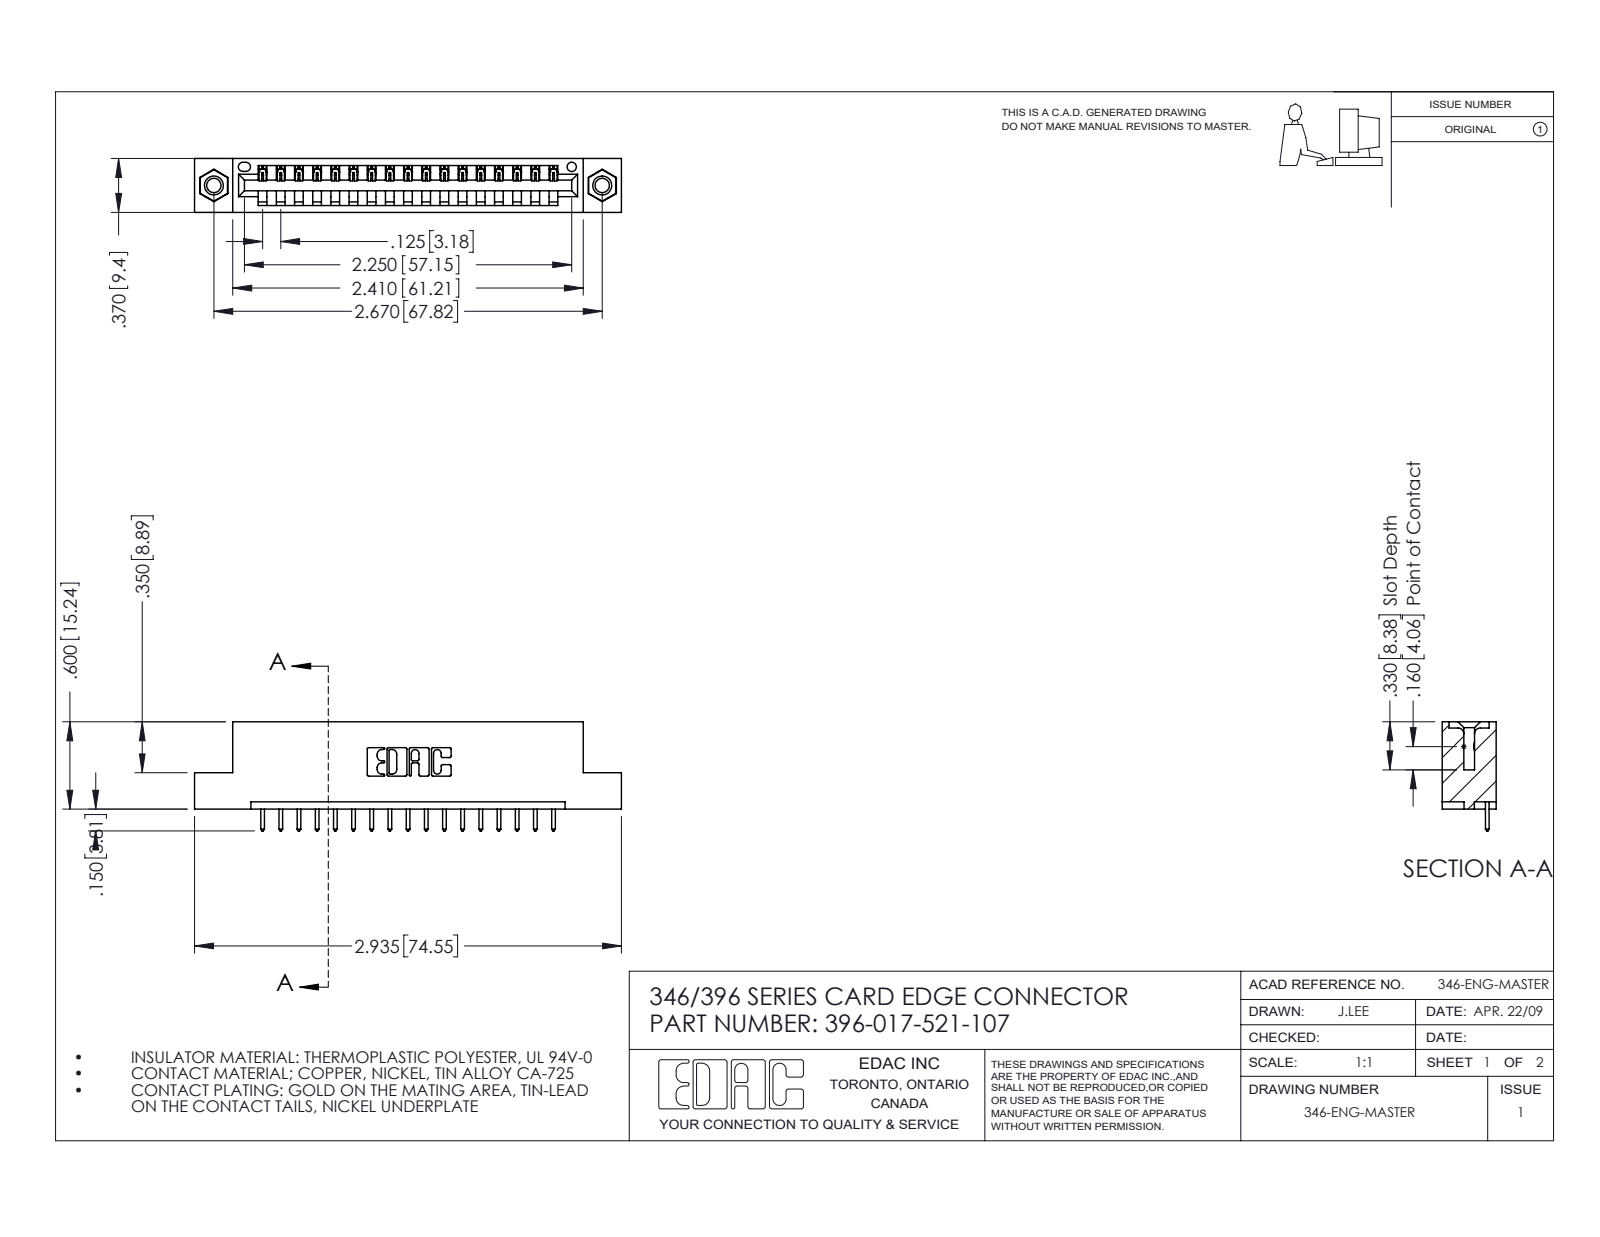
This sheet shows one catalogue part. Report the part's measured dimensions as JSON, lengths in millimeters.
{"part_name": "346 Part_Flush Mounting Lugs - 0.156 Dia-TI; 396-017-521-107; 345-250-001_345-250-005-103; 345-292-001_345-293-121", "step_written_by": "SolidWorks 2016 (CONFIG_CONTROL_DESIGN)", "units": "millimeters", "bodies": {"solids": 20, "faces": 1168, "planar": 788, "cylindrical": 364, "other": 16}, "overall_size": [74.5, 19.1, 9.4], "volume_mm3": 6900, "surface_area_mm2": 8200, "round_holes": [[2.5, 2], [3.2, 2], [4, 2], [1.6, 1]], "round_bosses_or_shafts": [[3.9, 2]], "partial_cylinders_radius": [[0.2, 34], [0.3, 34], [0.3, 22], [0.2, 6], [0.8, 6], [0.7, 3], [0.8, 2], [1, 2]], "face_to_face_distances": [1.2, 8.2, 9.4, 6.4, 1.8, 7.6, 0.6, 3.8, 5.6, 2.5], "hole_center_spacings": [6.2, 62.6, 67.8]}
